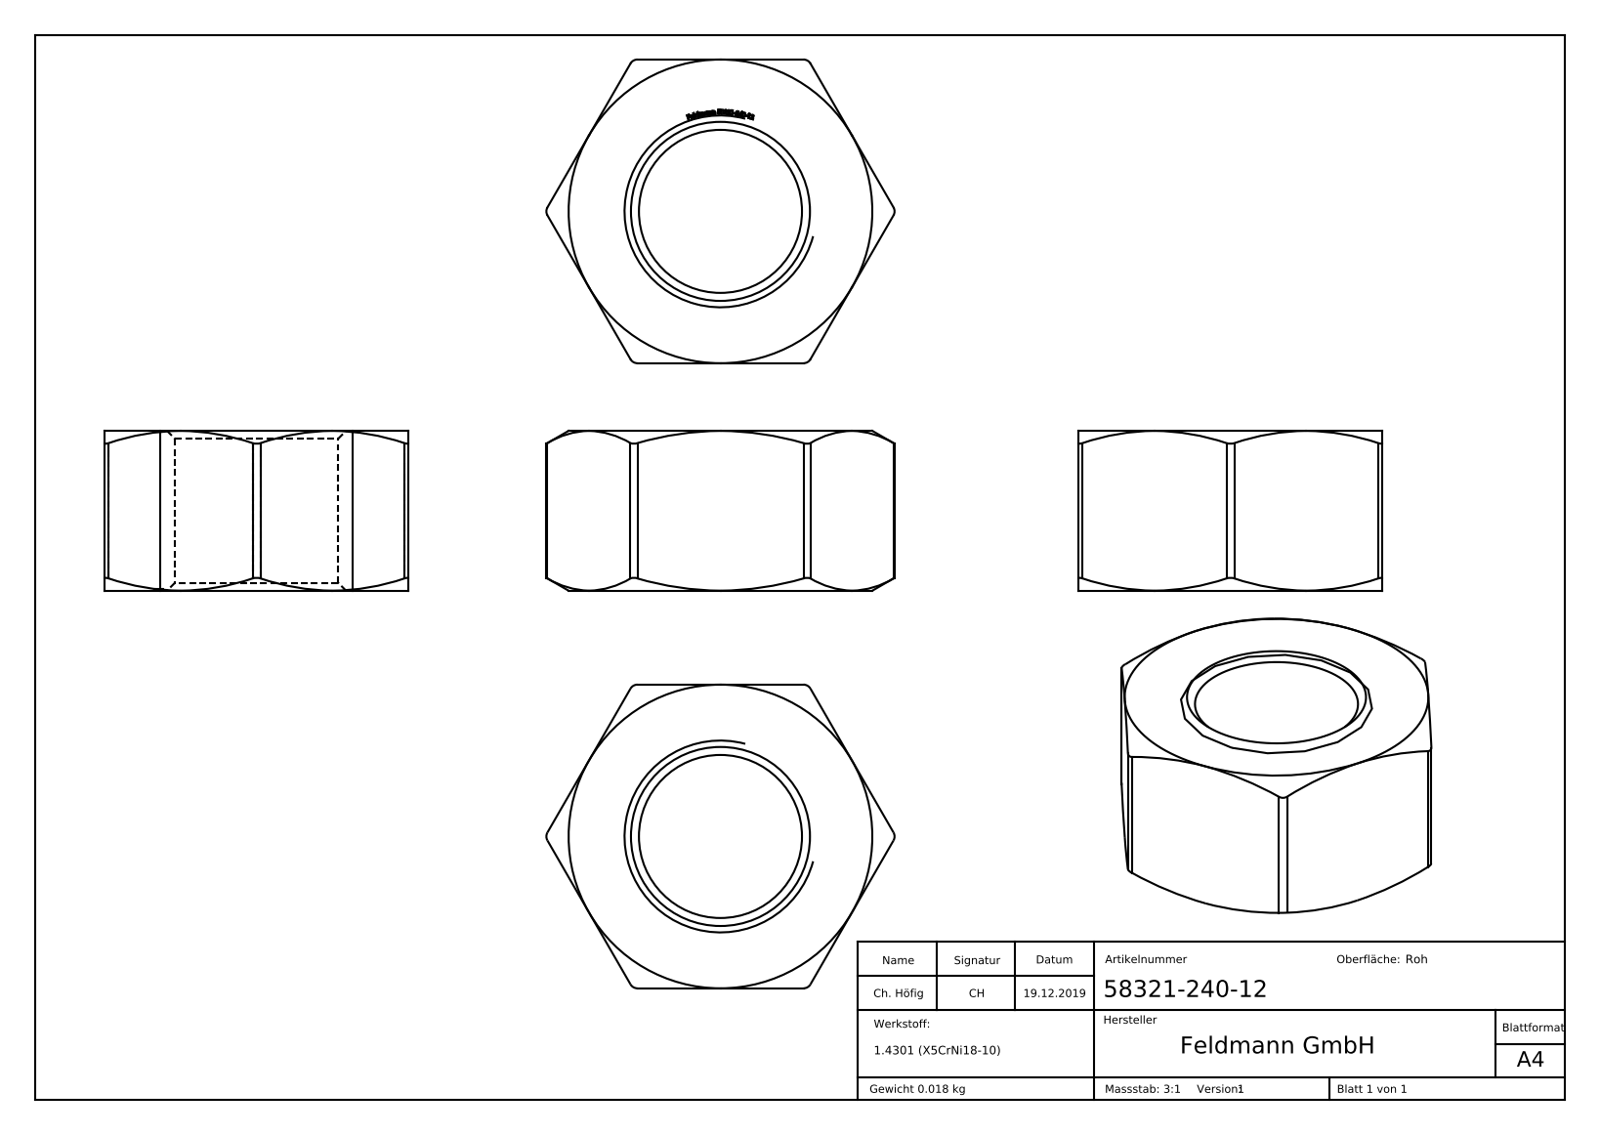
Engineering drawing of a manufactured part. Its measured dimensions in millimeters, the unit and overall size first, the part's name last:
Units: millimetres
Overall size (bounding box): 22 × 21.79 × 19
Round holes (diameter × count): ⌀10.2 ×1
Partial cylindrical surfaces — rounded edges, fillets, slot ends (radius × count): R0.5 ×6
Main face-to-face distances: 19, 10, 9.9
Volume: 2 285 mm³ · Surface area: 1 392 mm²
Bodies: 1 solid, 284 faces (149 planar, 7 cylindrical, 128 other)
Part name (STEP PRODUCT): 58321-240-12
STEP written by: SolidWorks 2015 (CONFIG_CONTROL_DESIGN)
